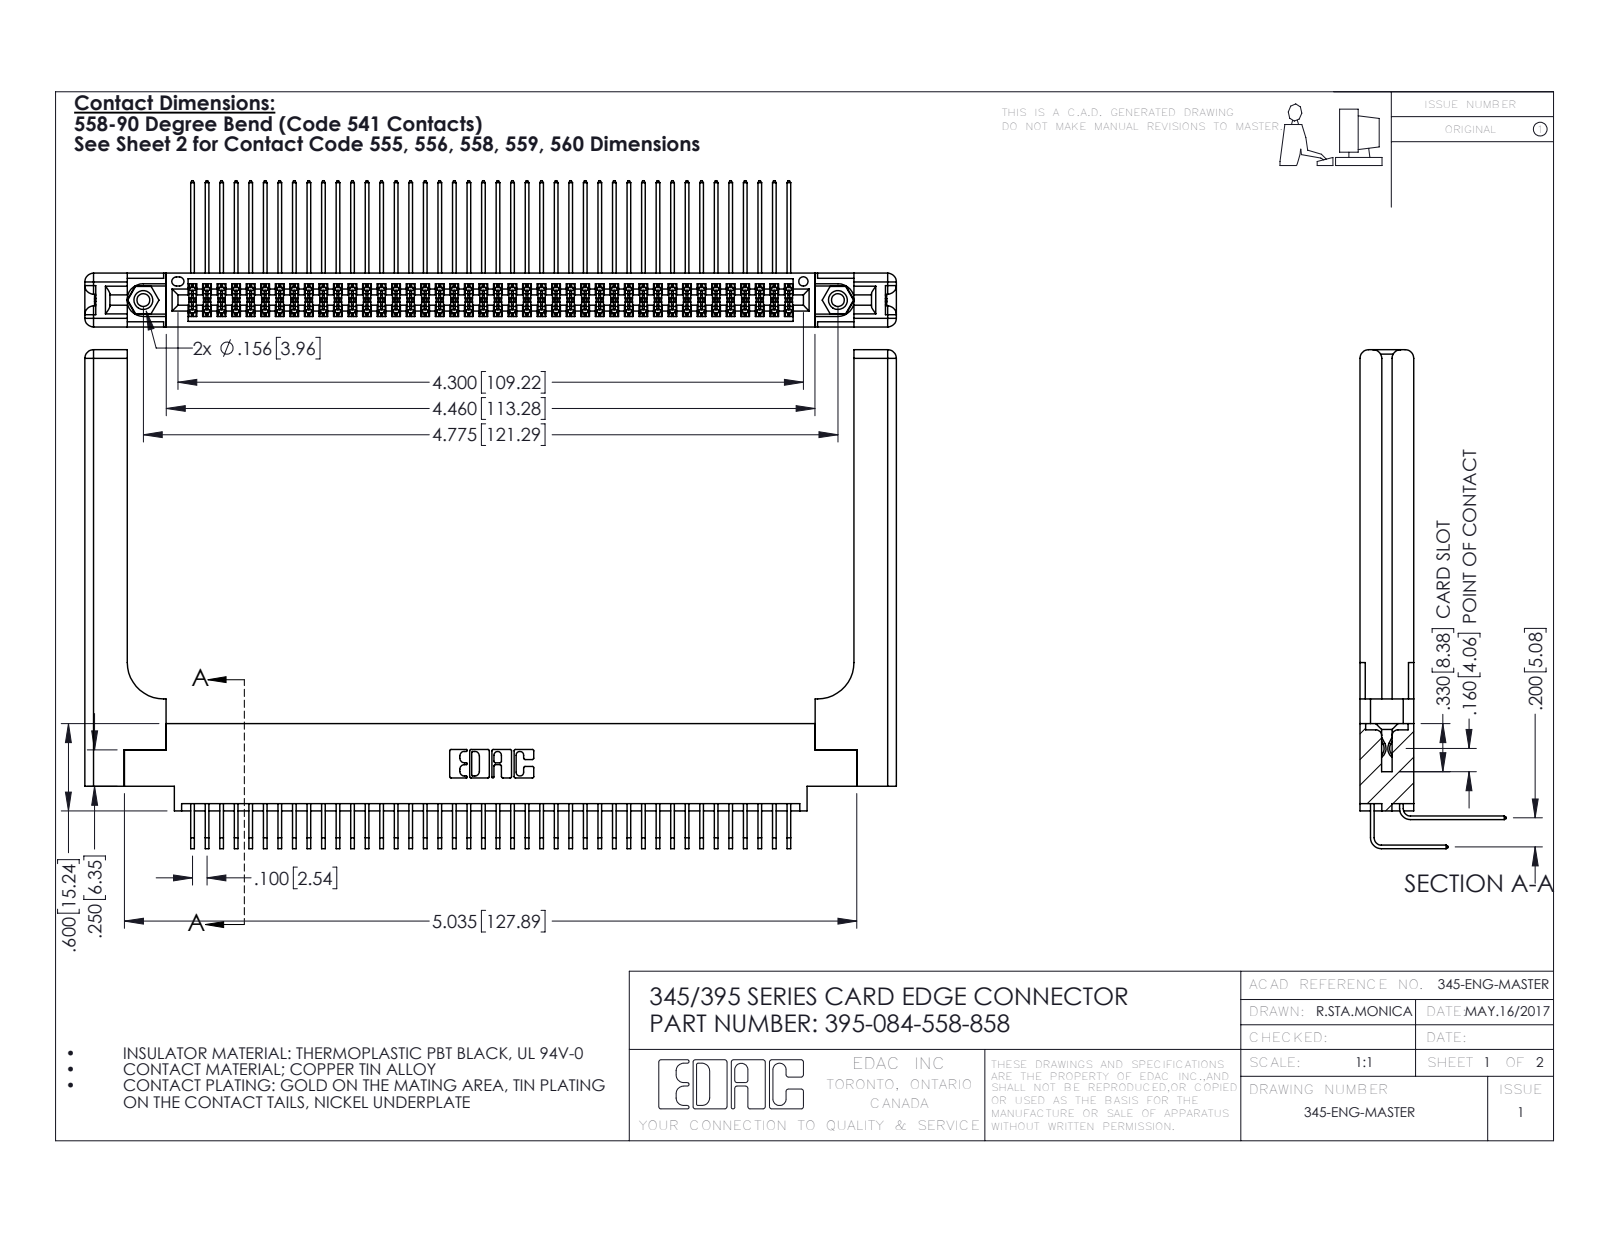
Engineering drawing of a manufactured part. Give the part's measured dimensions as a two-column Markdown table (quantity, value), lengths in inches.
| quantity | value |
| --- | --- |
| part name | 345-292-001_558 559 Tail - 1; 345-220-058_345-220-058; 345-292-001_558 Tail - 2; 345-250-001_345-250-001-102 (+2 more) |
| STEP written by | SolidWorks 2016 (CONFIG_CONTROL_DESIGN) |
| units | inches |
| bodies | 89 solids, 4754 faces (3172 planar, 1522 cylindrical, 60 other) |
| overall size | 5.579 × 3.429 × 1.005 |
| volume | 1.38 in³ |
| surface area | 43.99 in² |
| round holes (diameter × count) | 0.089 × 2, 0.125 × 2, 0.156 × 2, 0.064 × 1 |
| round bosses / shafts (diameter × count) | 0.155 × 2 |
| partial cylindrical surfaces (radius × count) | 0.006 × 127, 0.01 × 22, 0.06 × 16, 0.007 × 6, 0.031 × 6, 0.026 × 3, 0.014 × 2, 0.019 × 2 |
| main face-to-face distances | 0.072, 0.37, 0.298, 0.2, 0.098, 0.272, 0.025, 0.225, 0.148, 0.15 |
| hole center spacings | 0.27, 4.539, 4.775 |
